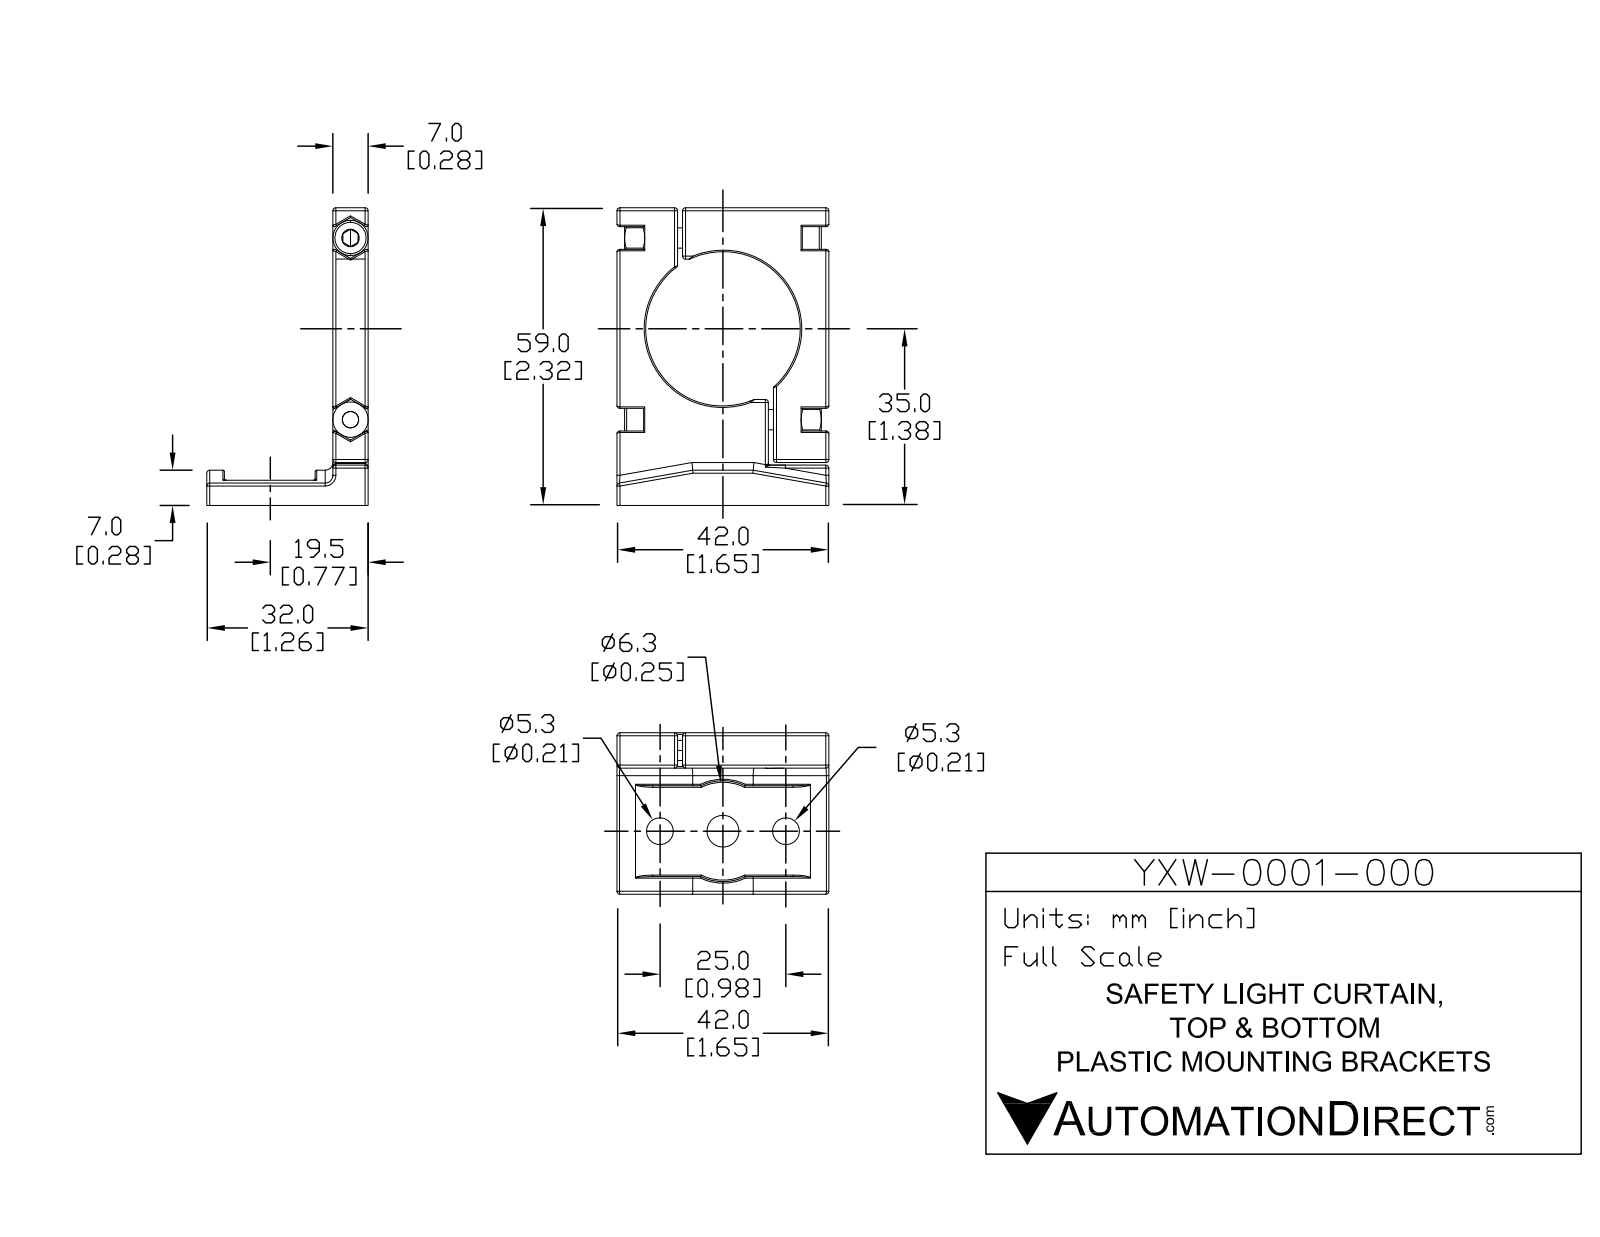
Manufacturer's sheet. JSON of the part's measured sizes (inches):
{"part_name": "YXW-0001-000", "step_written_by": "SolidWorks 2021 (AUTOMOTIVE_DESIGN)", "units": "inches", "bodies": {"solids": 2, "faces": 186, "planar": 134, "cylindrical": 48, "other": 4}, "overall_size": [2.323, 1.654, 1.26], "volume_in3": 0.971, "surface_area_in2": 15.88, "round_holes": [[0.209, 2], [0.248, 1], [1.205, 1]], "round_bosses_or_shafts": [[0.157, 2], [0.276, 1], [0.276, 1]], "partial_cylinders_radius": [[0.024, 12], [0.012, 5], [0.177, 2], [0.118, 1], [0.197, 1], [0.394, 1]], "face_to_face_distances": [0.276, 0.059, 0.197, 0.138, 0.098, 1.654, 0.984, 0.039, 0.217, 1.26], "hole_center_spacings": [0.492, 0.984]}
